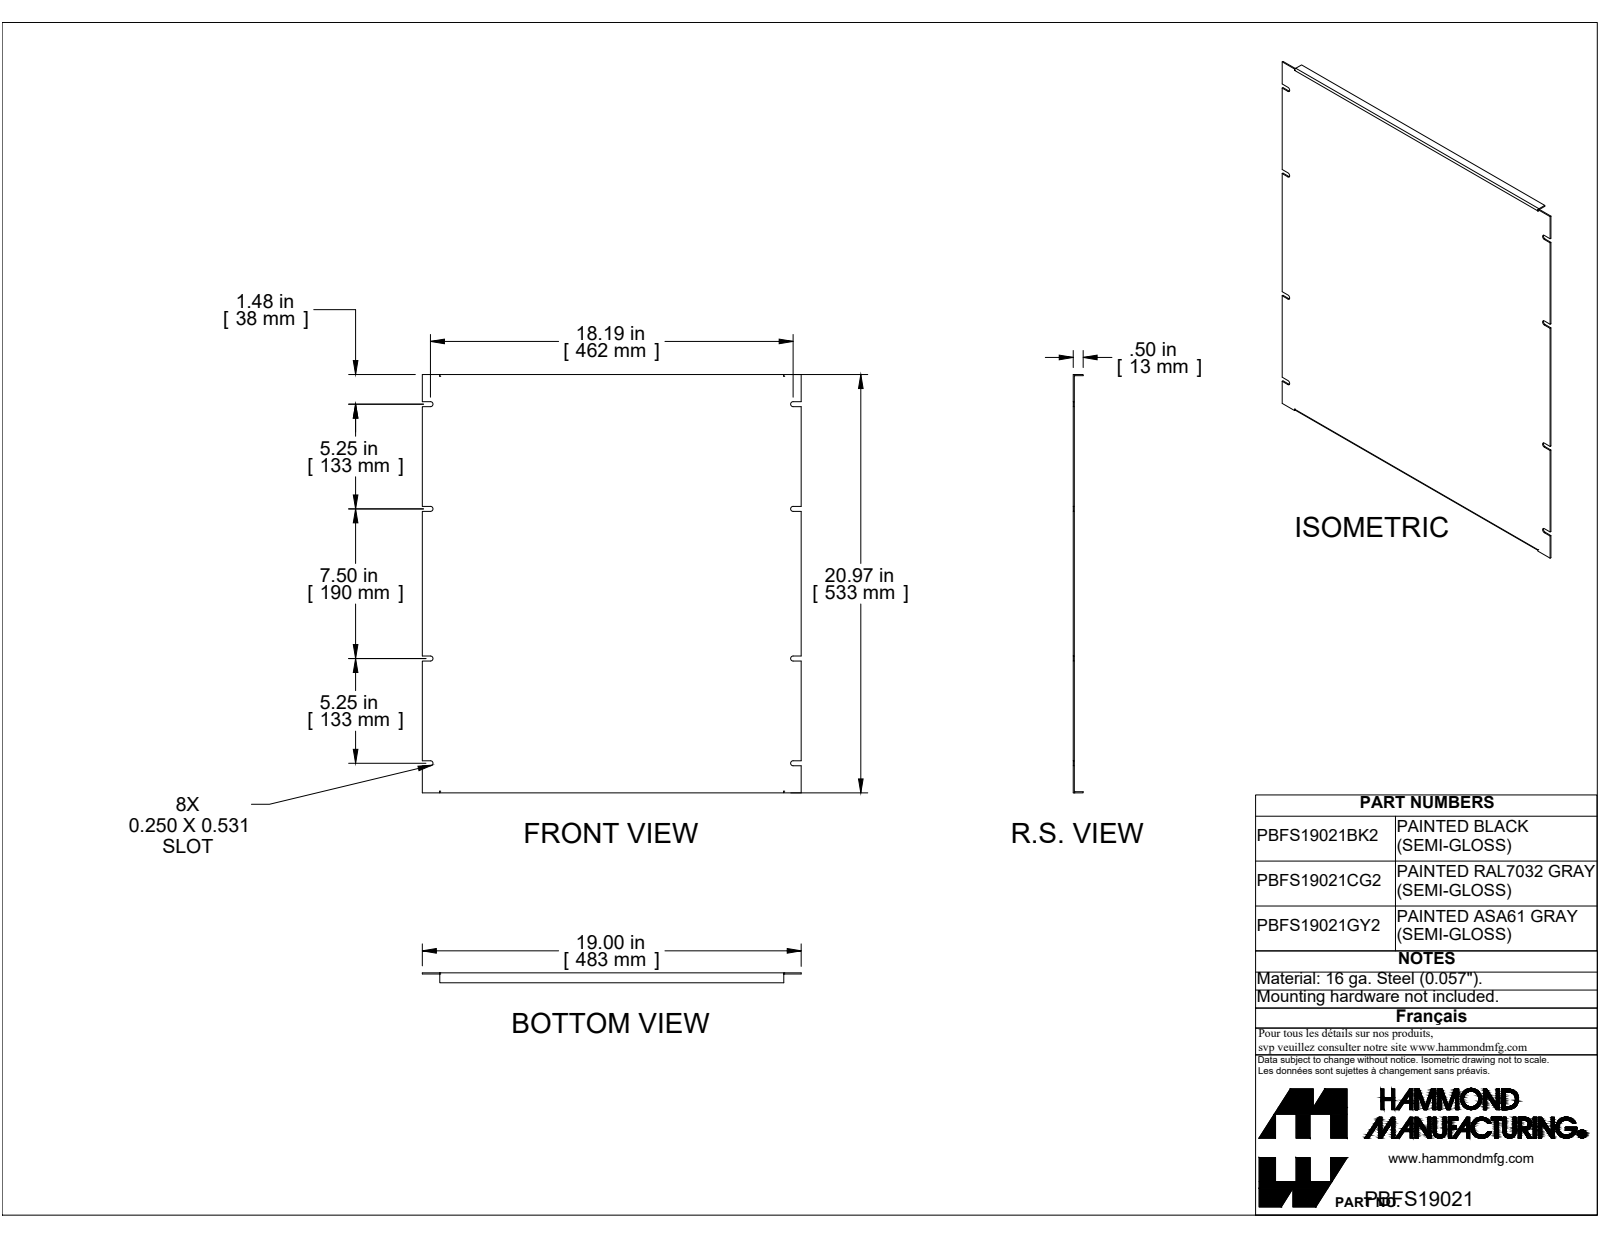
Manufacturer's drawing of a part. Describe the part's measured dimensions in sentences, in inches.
The part is named "PBFS19021". Its 3-D file was written by "SolidWorks 2019 (CONFIG_CONTROL_DESIGN)". It is 1 solid with 62 faces: 50 planar, 12 cylindrical and 0 other. Overall it measures 20.968 by 19 by 0.5 inches. Its volume is 23.47 cubic inches and its surface area 828.8 square inches. Partial cylindrical surfaces (rounded edges, fillets, slot ends): 8 of radius 0.125, 2 of radius 0.029, 2 of radius 0.086. The main face-to-face distances are 0.057, 0.057, 20.911, 20.968, 20.854, 0.5, 0.443, 19, 0.875, 18.125.
